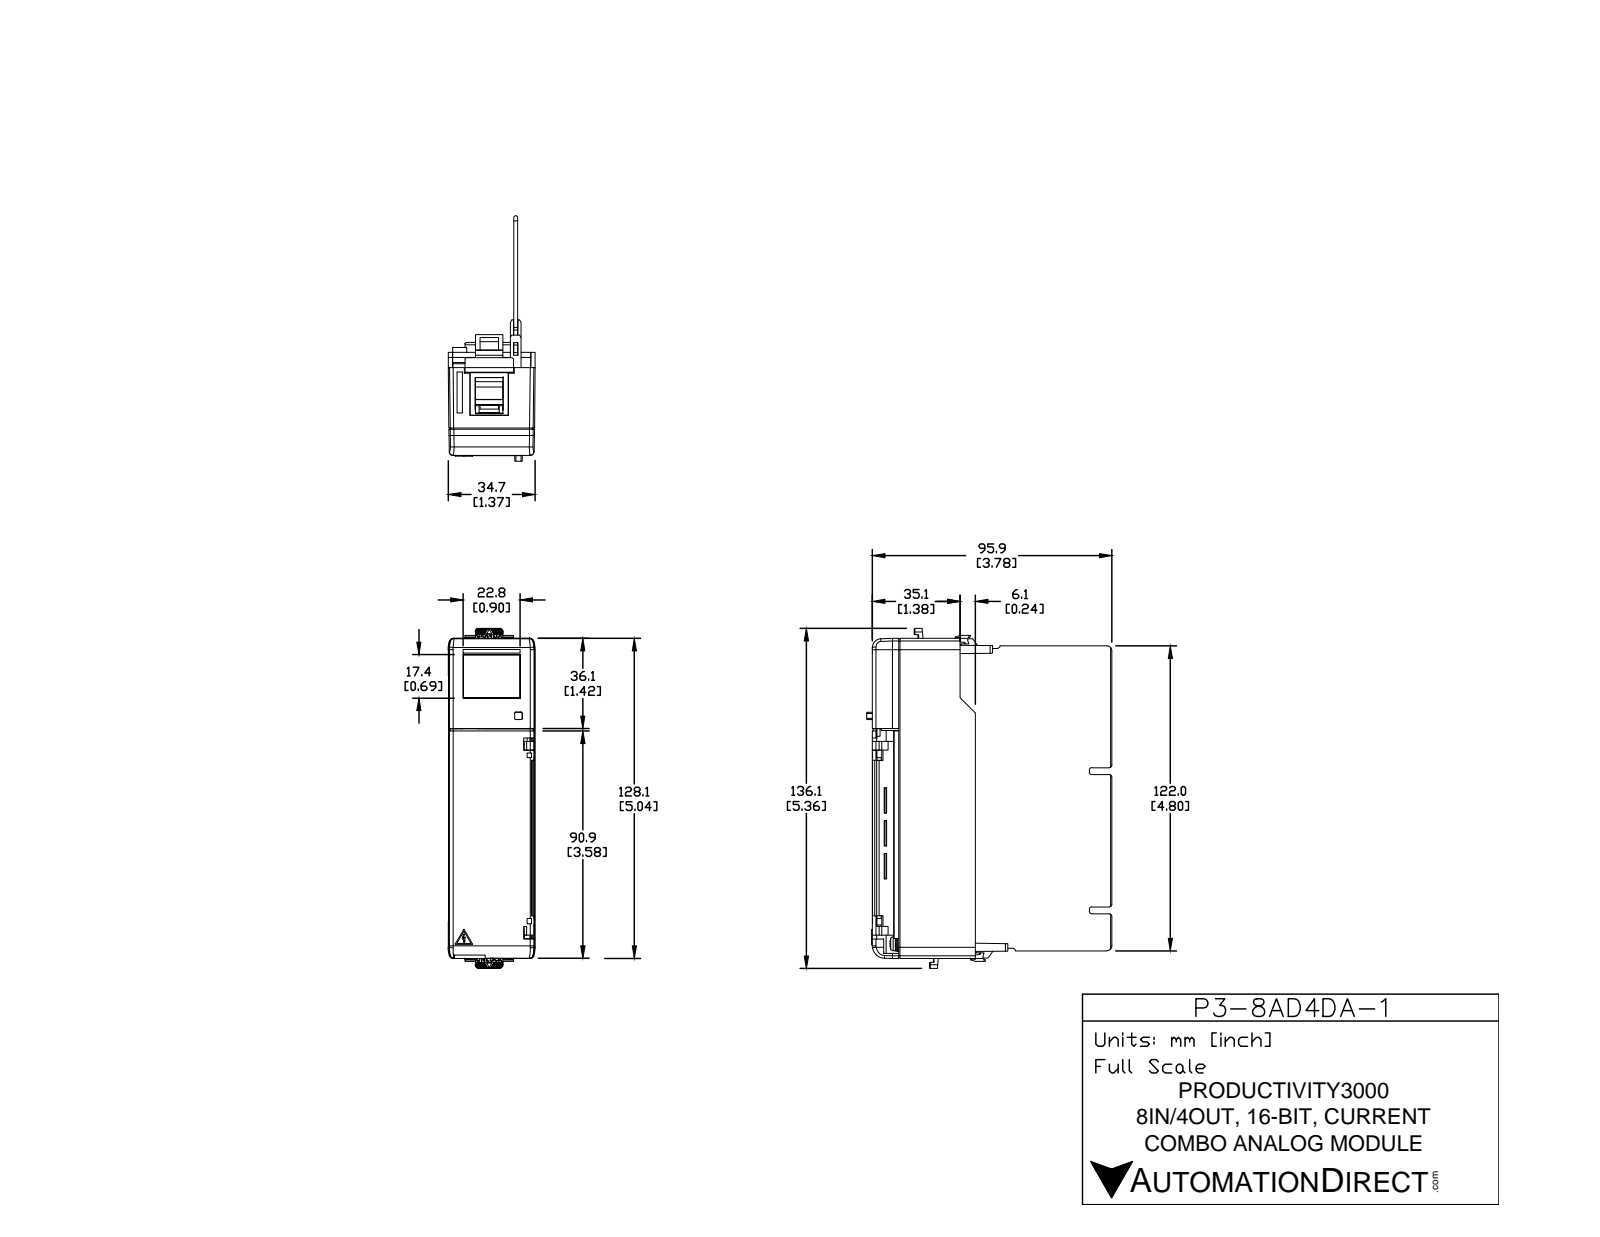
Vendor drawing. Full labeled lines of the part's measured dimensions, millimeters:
Part name (STEP PRODUCT): P3-8AD4DA-1
STEP written by: SolidWorks 2009 (CONFIG_CONTROL_DESIGN)
Units: millimetres
Bodies: 1 solid, 3823 faces (2833 planar, 744 cylindrical, 246 other)
Overall size (bounding box): 136.08 × 98.18 × 34.8
Volume: 101 360 mm³ · Surface area: 75 361 mm²
Round holes (diameter × count): ⌀3.2 ×22, ⌀5 ×2, ⌀1.8 ×1
Round bosses / shafts (diameter × count): ⌀5.5 ×22, ⌀3 ×22, ⌀2.4 ×20, ⌀5.6 ×2, ⌀2.2 ×2, ⌀2 ×2, ⌀1.5 ×1
Partial cylindrical surfaces — rounded edges, fillets, slot ends (radius × count): R0.5 ×95, R1 ×33, R0.3 ×29, R1.67 ×22, R1.5 ×13, R2 ×6, R0.2 ×5, R0.1 ×4
Main face-to-face distances: 1.6, 1.7, 28.23, 26.53, 32.56, 22.2, 2.2, 7.9, 6.8, 5.32
Hole centre spacings: 8.68, 7.62, 13.84, 15.24, 20.59, 22.86, 27.79, 30.48
